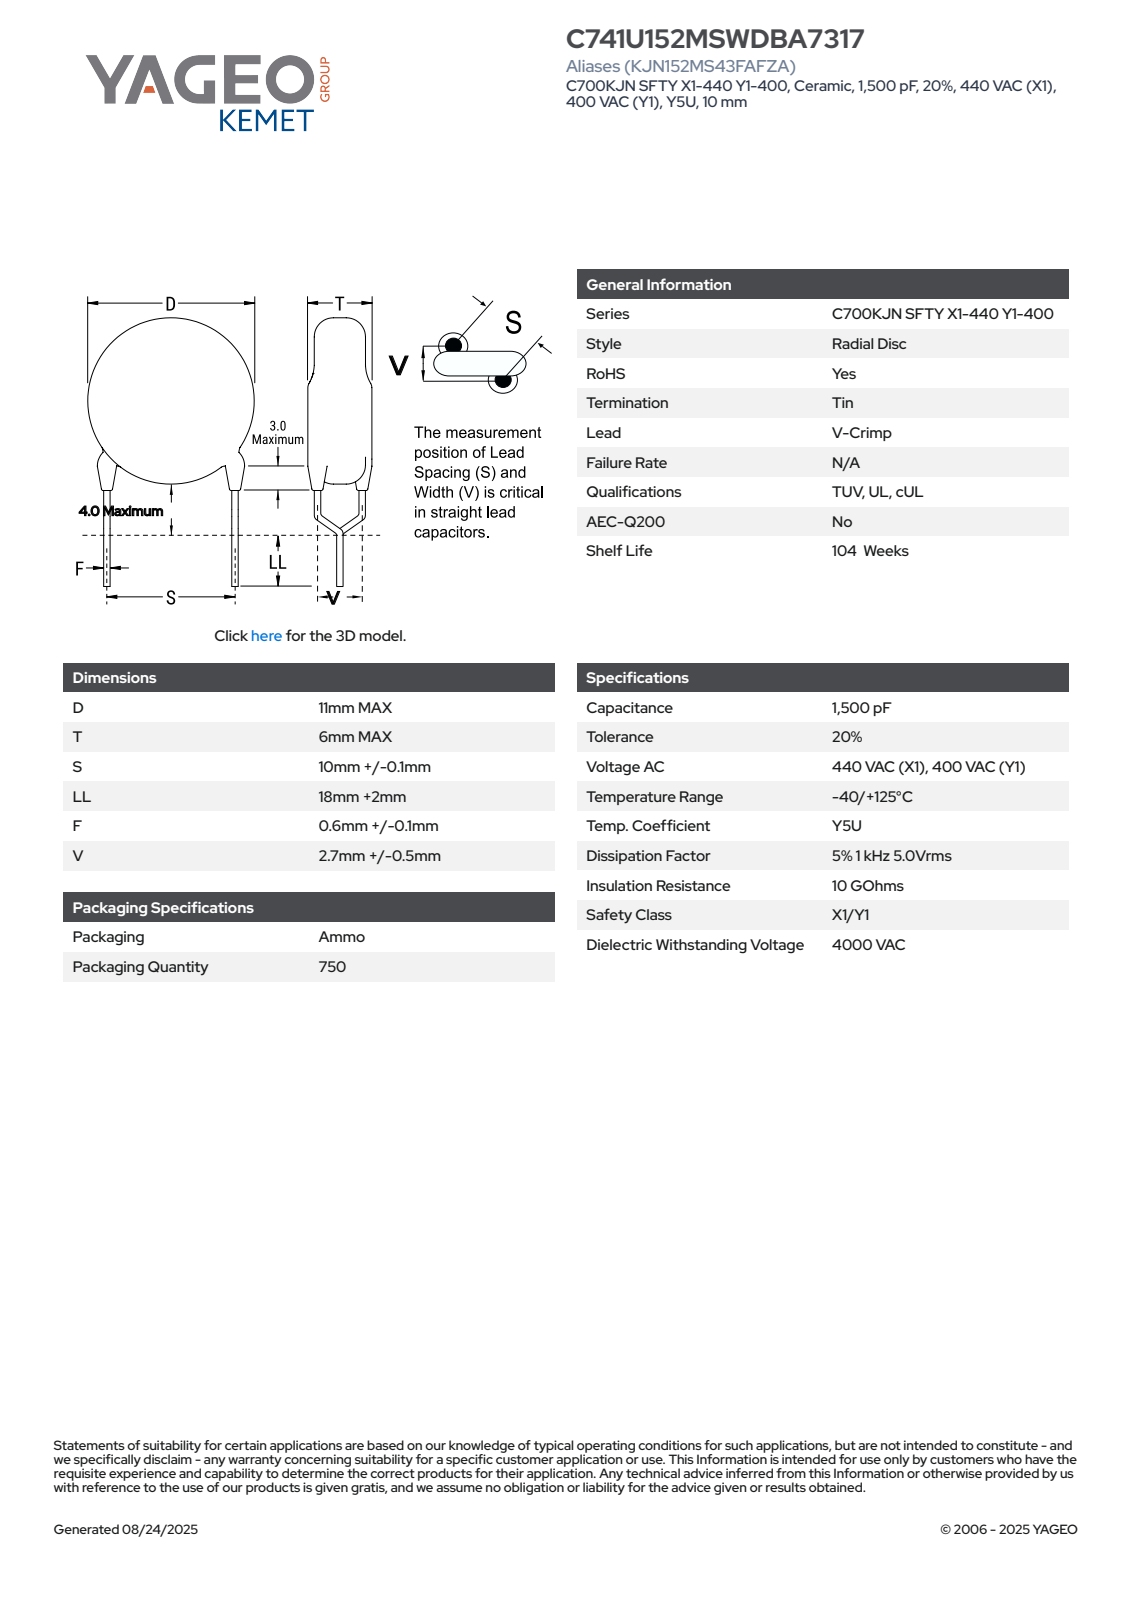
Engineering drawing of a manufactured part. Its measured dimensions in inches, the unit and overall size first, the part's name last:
Units: inches
Overall size (bounding box): 1.22 × 0.441 × 0.236
Round bosses / shafts (diameter × count): ⌀0.028 ×6, ⌀0.047 ×4, ⌀0.433 ×1
Main face-to-face distances: 0.236, 0.787, 0.038, 1.024, 0.237, 0.986, 0.198, 0.017, 0.024, 0.156
Volume: 0.035 in³ · Surface area: 0.752 in²
Bodies: 4 solids, 89 faces (63 planar, 22 cylindrical, 4 other)
Part name (STEP PRODUCT): CCD_VC11X6_D11T6S10LL20F0.7V2.7
STEP written by: SolidWorks 2021 (AUTOMOTIVE_DESIGN)
